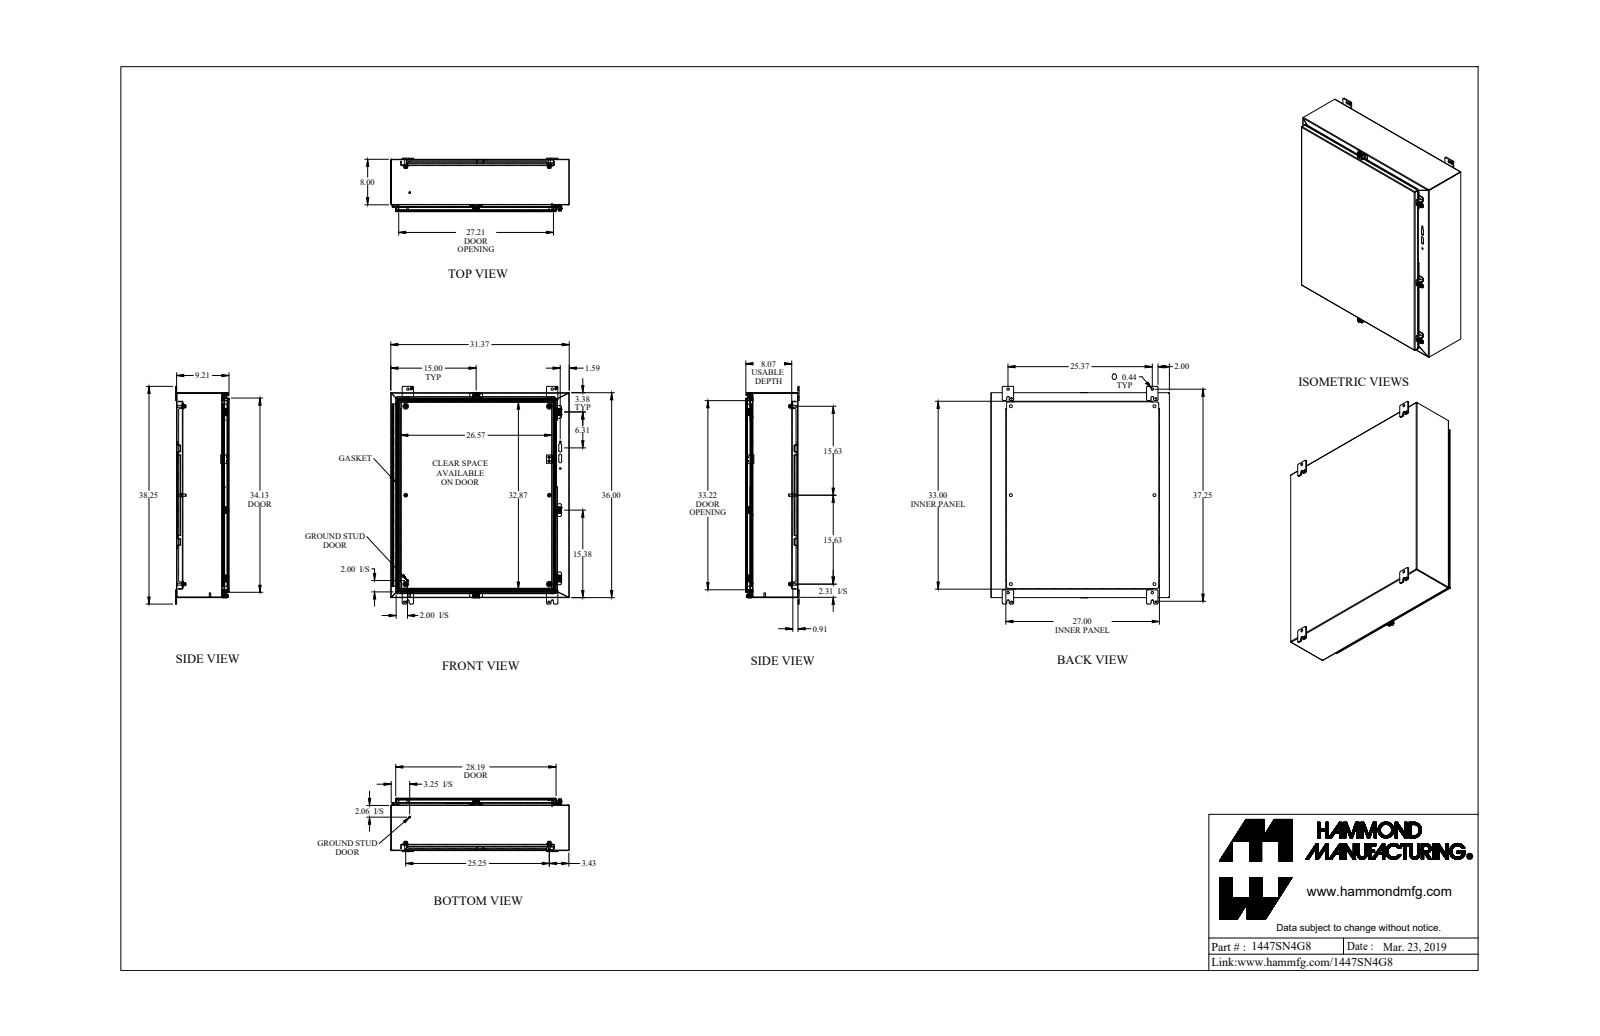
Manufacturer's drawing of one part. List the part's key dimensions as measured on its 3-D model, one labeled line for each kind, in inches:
Part name (STEP PRODUCT): 1447SN4G8_Default
STEP written by: SolidWorks 2019 (CONFIG_CONTROL_DESIGN)
Units: inches
Bodies: 56 solids, 1858 faces (1082 planar, 664 cylindrical, 112 other)
Overall size (bounding box): 38.25 × 31.372 × 9.397
Volume: 390 in³ · Surface area: 10 190 in²
Round holes (diameter × count): ⌀0.313 ×6, ⌀0.5 ×6, ⌀0.213 ×5, ⌀0.265 ×5, ⌀0.375 ×5, ⌀0.307 ×4, ⌀0.437 ×4, ⌀0.445 ×4, ⌀0.15 ×2, ⌀0.156 ×2, ⌀0.281 ×2, ⌀0.187 ×1
Round bosses / shafts (diameter × count): ⌀0.65 ×6, ⌀0.375 ×6, ⌀0.33 ×6, ⌀0.5 ×5, ⌀0.39 ×5, ⌀0.244 ×5, ⌀1 ×4, ⌀0.25 ×4
Partial cylindrical surfaces — rounded edges, fillets, slot ends (radius × count): R0.25 ×36, R0.188 ×32, R0.048 ×27, R0.143 ×27, R0.036 ×22, R0.108 ×22, R0.116 ×12, R0.045 ×10
Main face-to-face distances: 0.072, 9.066, 9.138, 0.072, 9.138, 9.21, 0.095, 8.106, 8.034, 1.032
Hole centre spacings: 27.141, 15.625, 25.25, 25.372, 29.694, 43.838, 2.122, 12.559
